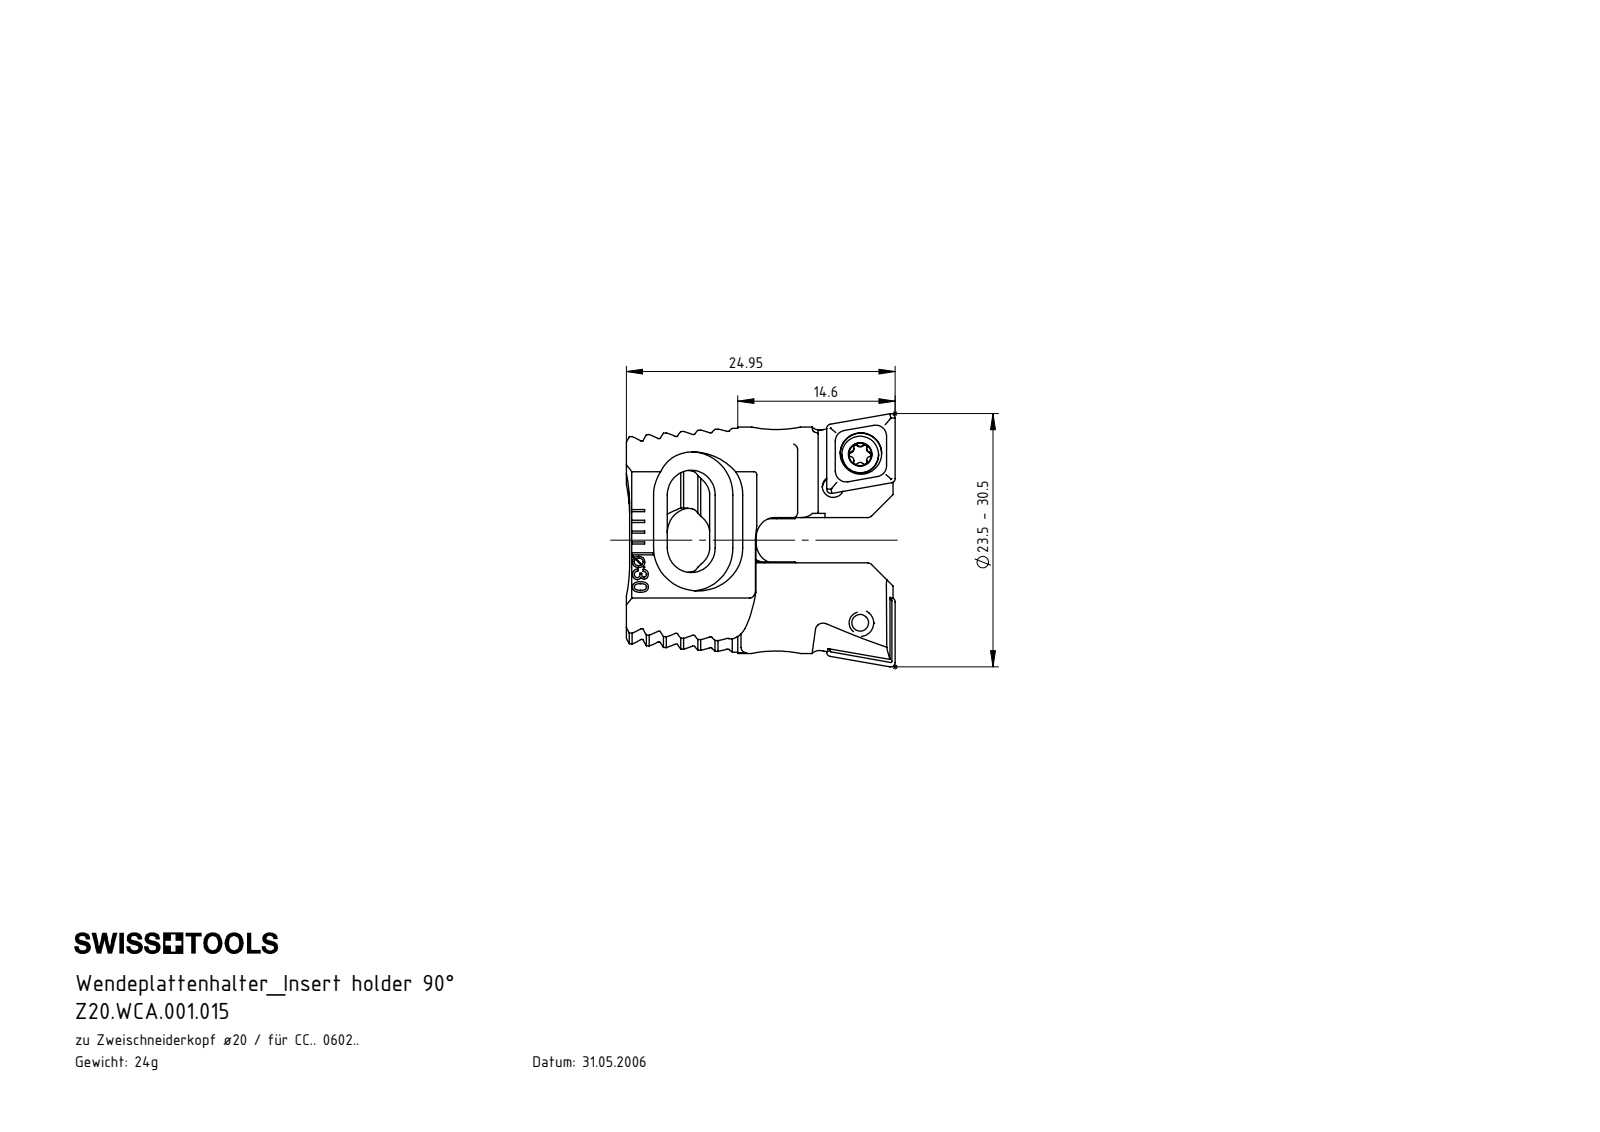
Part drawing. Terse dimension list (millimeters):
name: Z20-xxx.001.015_D; WCA-ER2.001.006_A; Z20-ER3.001.007_A; Z20.WCA.001.015 (+1 more)
written by: SolidWorks 2022 (AUTOMOTIVE_DESIGN)
unit: mm
bodies: 8 solids, 606 faces (262 planar, 134 cylindrical, 210 other)
size: 24.95 × 23.5 × 16.2
volume: 2 962 mm³; area: 3 413 mm²
holes: 2× ⌀1.6, 2× ⌀2, 2× ⌀2.05, 2× ⌀2.8, 2× ⌀3.85, 1× ⌀3.5, 1× ⌀9.1
bosses: 2× ⌀3.4, 2× ⌀2.5, 1× ⌀4
rounds: 16× R0.5, 12× R0.12, 12× R0.21, 8× R0.36, 4× R0.36, 4× R1, 4× R2, 4× R2.3
face distances: 1.43, 2.86, 4.29, 3.79, 0.4, 4.6, 5.71, 5.72, 2.97, 6.76
hole spacings: 3.91, 4.01, 5.5, 13.15, 13.24, 15.98, 9.91, 10.62
